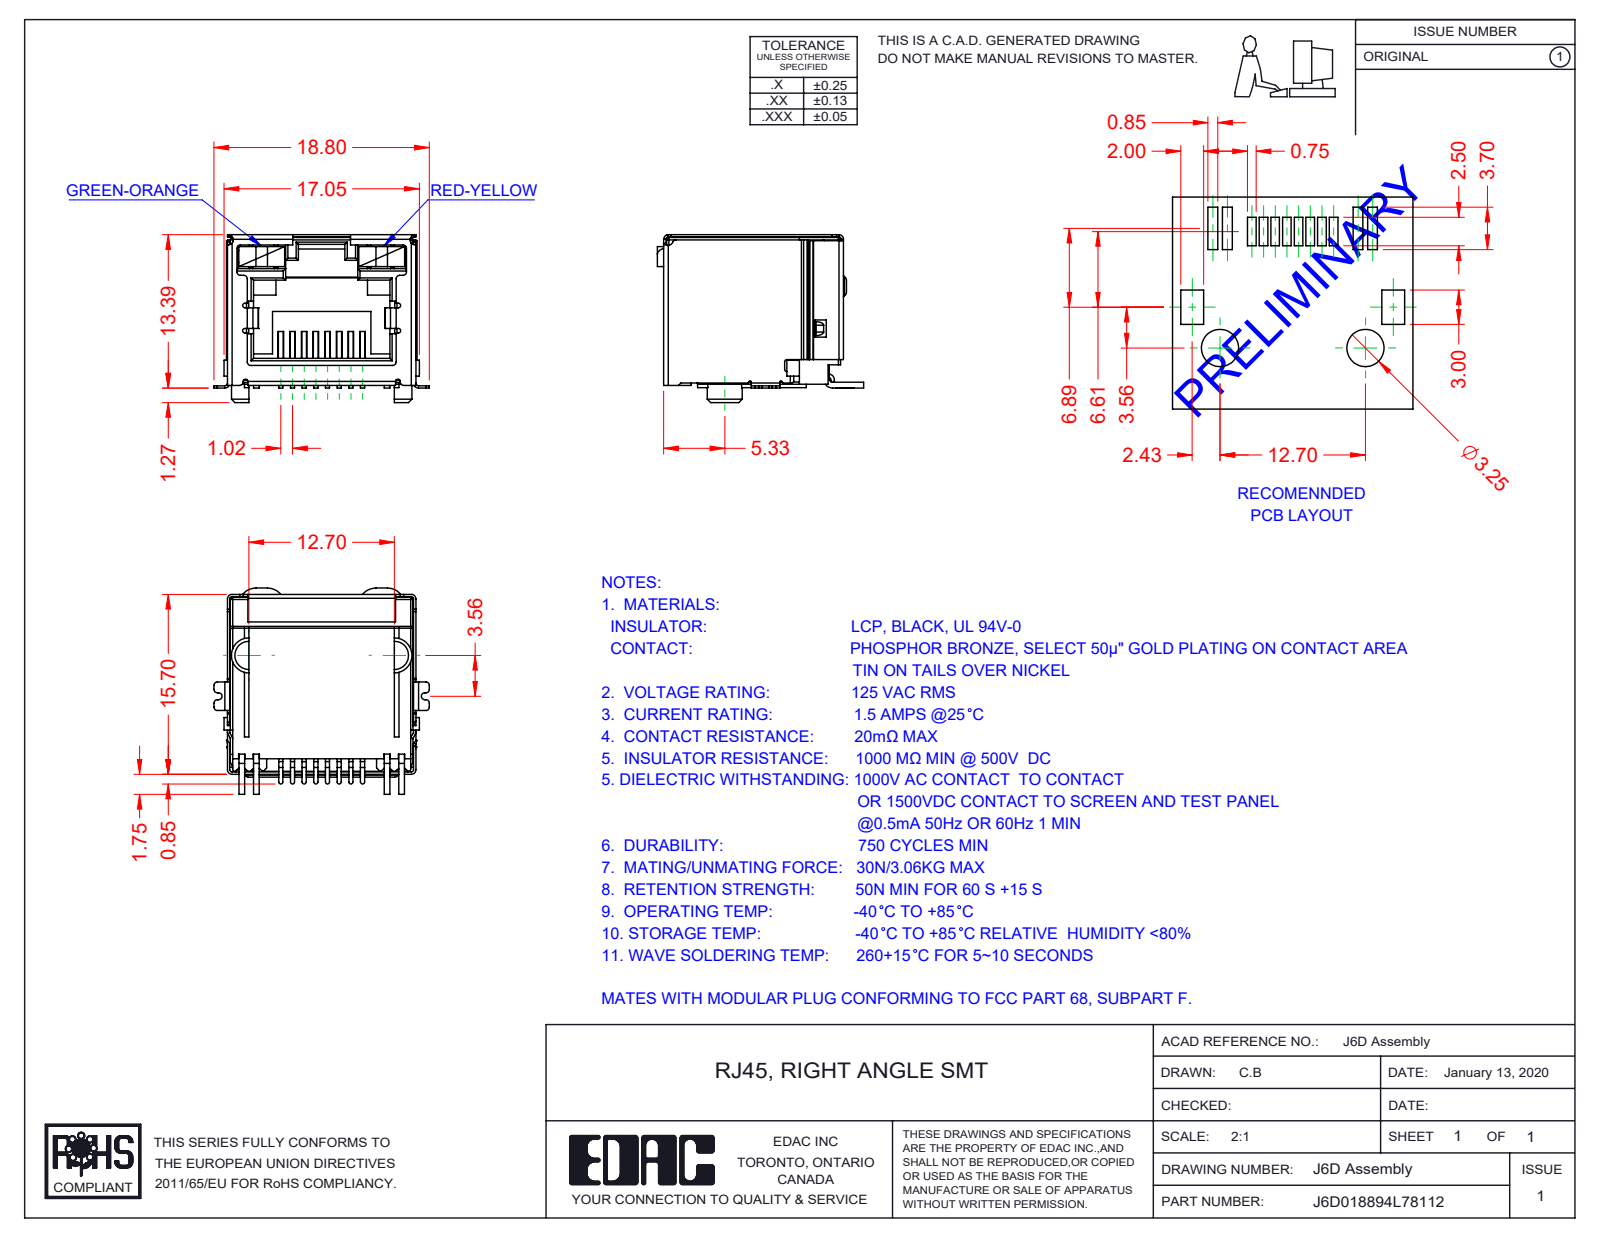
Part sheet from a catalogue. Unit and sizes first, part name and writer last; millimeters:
Units: millimetres
Overall size (bounding box): 18.8 × 18 × 14.65
Partial cylindrical surfaces — rounded edges, fillets, slot ends (radius × count): R0.3 ×39, R0.2 ×37, R0.4 ×16, R0.1 ×12, R0.15 ×8, R0.18 ×8, R0.5 ×6, R1.5 ×5
Main face-to-face distances: 16, 16.25, 16.2, 2.25, 1, 15.95, 16.05, 12.8, 0.45, 16.45
Volume: 1 804 mm³ · Surface area: 4 898 mm²
Bodies: 12 solids, 899 faces (646 planar, 220 cylindrical, 33 other)
Part name (STEP PRODUCT): J6D018894L78112; 6D LED RH_8-Red-Yellow; 6D LED LH_7-Green-Orange; 6D Contacts (+2 more)
STEP written by: SolidWorks 2016 (CONFIG_CONTROL_DESIGN)
